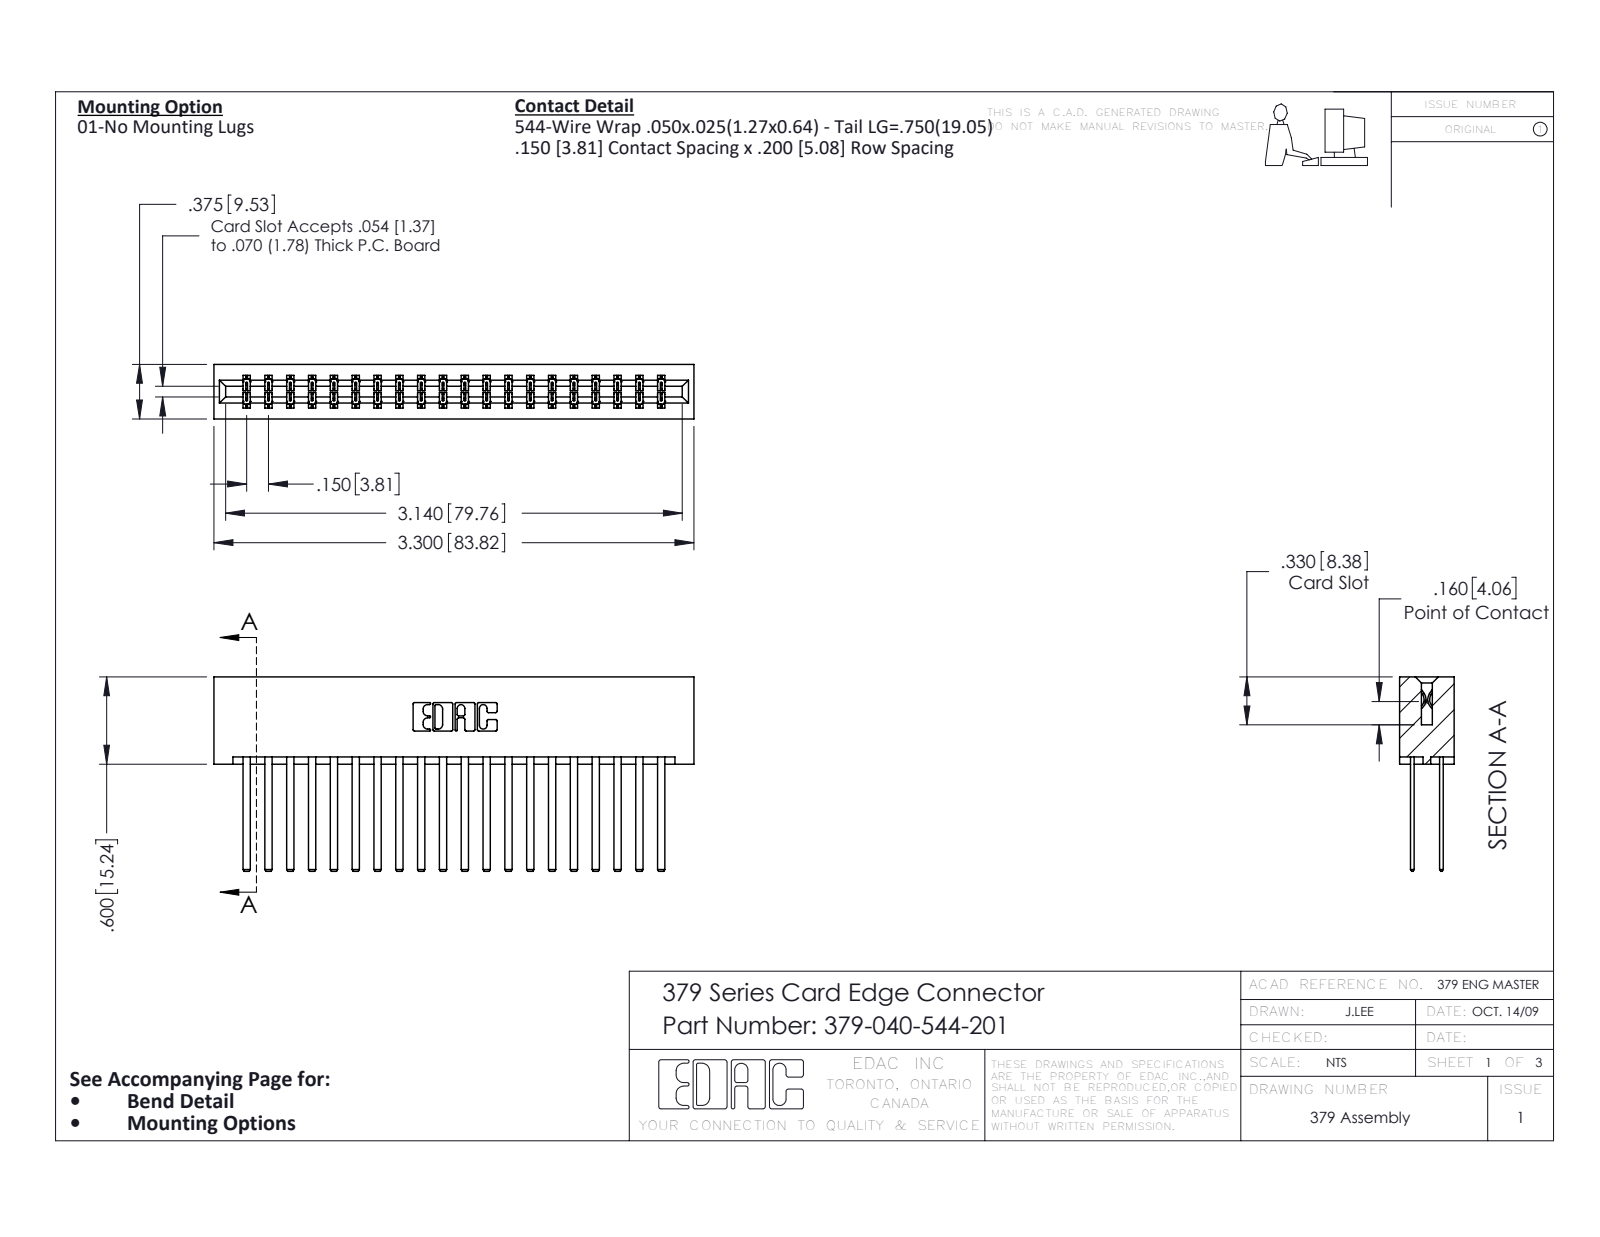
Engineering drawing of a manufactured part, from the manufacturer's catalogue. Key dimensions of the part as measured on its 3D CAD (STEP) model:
Part name (STEP PRODUCT): 379-040-544-201; 379 Part_Lugless; 345-292-001_345-293-144
STEP written by: SolidWorks 2016 (CONFIG_CONTROL_DESIGN)
Units: inches
Bodies: 41 solids, 1946 faces (1346 planar, 600 cylindrical, 0 other)
Overall size (bounding box): 3.3 × 1.337 × 0.375
Volume: 0.608 in³ · Surface area: 19.93 in²
Partial cylindrical surfaces — rounded edges, fillets, slot ends (radius × count): R0.006 ×60, R0.01 ×22, R0.007 ×6, R0.031 ×6, R0.026 ×3, R0.014 ×2, R0.022 ×2, R0.024 ×2
Main face-to-face distances: 0.3, 0.1, 0.2, 0.075, 0.275, 0.15, 0.375, 0.025, 0.6, 0.45
